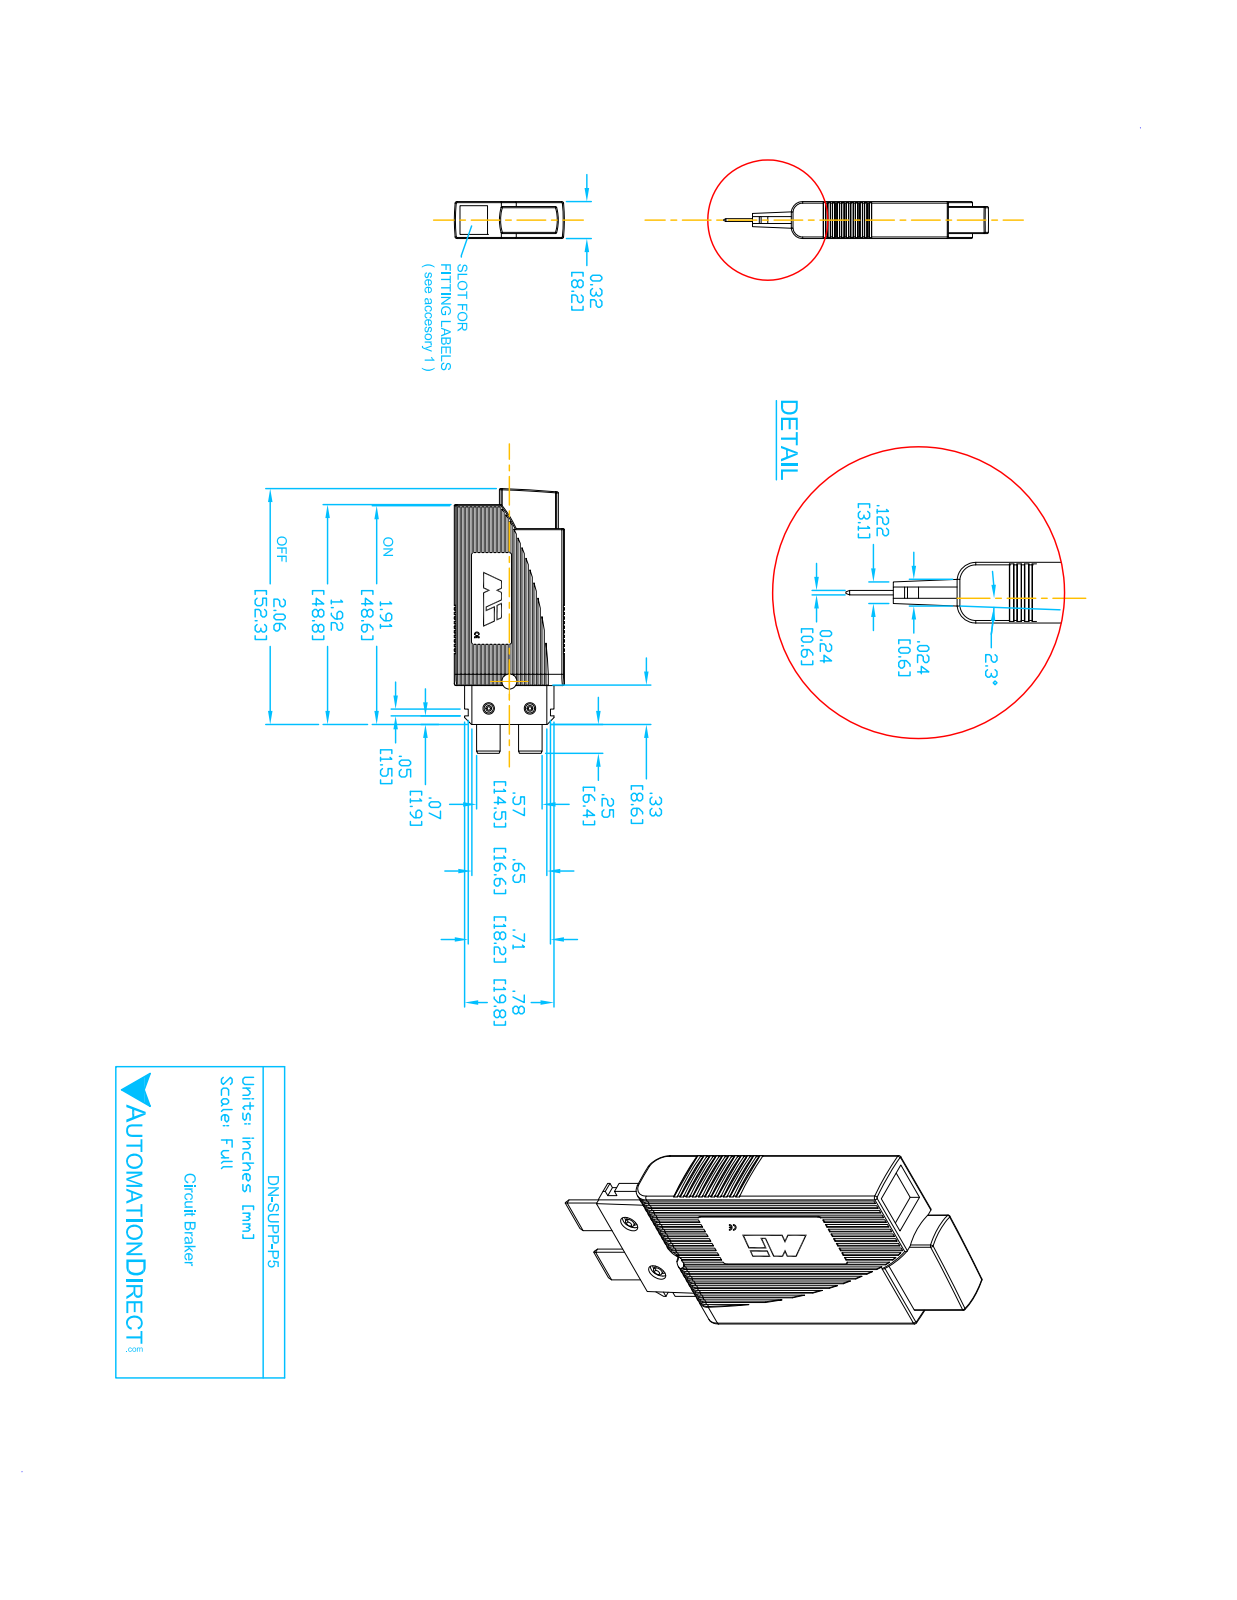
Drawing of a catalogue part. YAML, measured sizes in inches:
part_name: "DN-SUPP-P5"
step_written_by: "SolidWorks 2017 (AUTOMOTIVE_DESIGN)"
units: inches
bodies: {solids: 1, faces: 95, planar: 47, cylindrical: 28, other: 20}
overall_size: [2.18, 0.961, 0.323]
volume: 0.505
surface_area: 5.231
partial_cylinders:
  - {radius: 0.012, count: 21}
  - {radius: 0.157, count: 2}
  - {radius: 2.165, count: 1}
  - {radius: 2.331, count: 1}
  - {radius: 2.362, count: 1}
face_to_face_distances: [0.323, 0.961, 0.15, 0.173, 0.031, 0.291, 0.118, 0.142, 0.024, 0.14]
